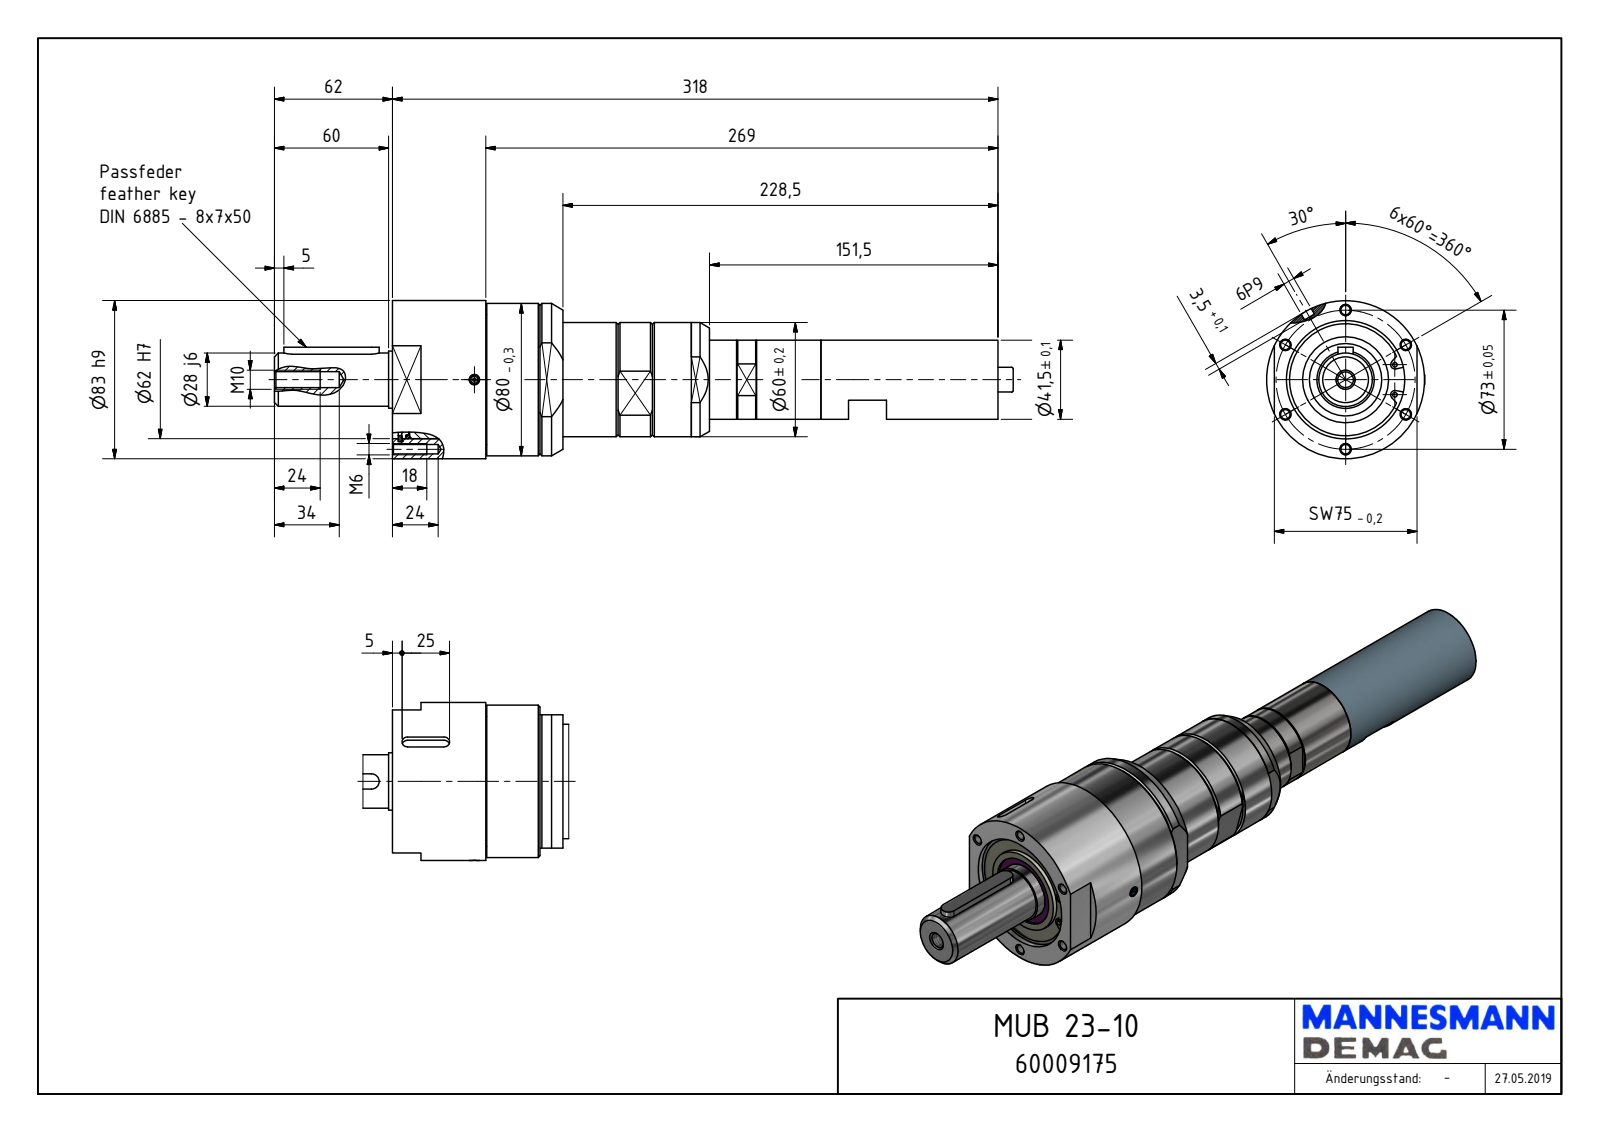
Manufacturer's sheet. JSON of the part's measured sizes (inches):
{"part_name": "MUB 32-10_60009175", "step_written_by": "Autodesk Inventor 2018 (AUTOMOTIVE_DESIGN)", "units": "inches", "bodies": {"solids": 1, "faces": 594, "planar": 205, "cylindrical": 312, "other": 77}, "overall_size": [15.276, 3.268, 3.268], "volume_in3": 54.56, "surface_area_in2": 153.2, "round_holes": [[0.194, 6], [0.061, 3], [0.098, 2], [0.157, 2], [0.217, 2], [0.337, 2], [0.33, 1], [0.335, 1], [1.437, 1], [1.496, 1], [1.555, 1], [1.575, 1]], "round_bosses_or_shafts": [[0.197, 2], [0.142, 2], [0.13, 2], [3.268, 1], [3.15, 1], [2.684, 1], [2.638, 1], [2.362, 1]], "partial_cylinders_radius": [[0.138, 94], [0.308, 7], [0.398, 3], [0.039, 2], [0.063, 2], [0.079, 2], [0.089, 2], [0.098, 2]], "face_to_face_distances": [1.929, 0.02, 8.996, 0.098, 5.965, 1.594, 3.524, 12.52, 10.591, 1.949], "hole_center_spacings": [1.437, 2.489, 2.874, 0.468, 1.054, 1.062, 1.517, 2.021]}
